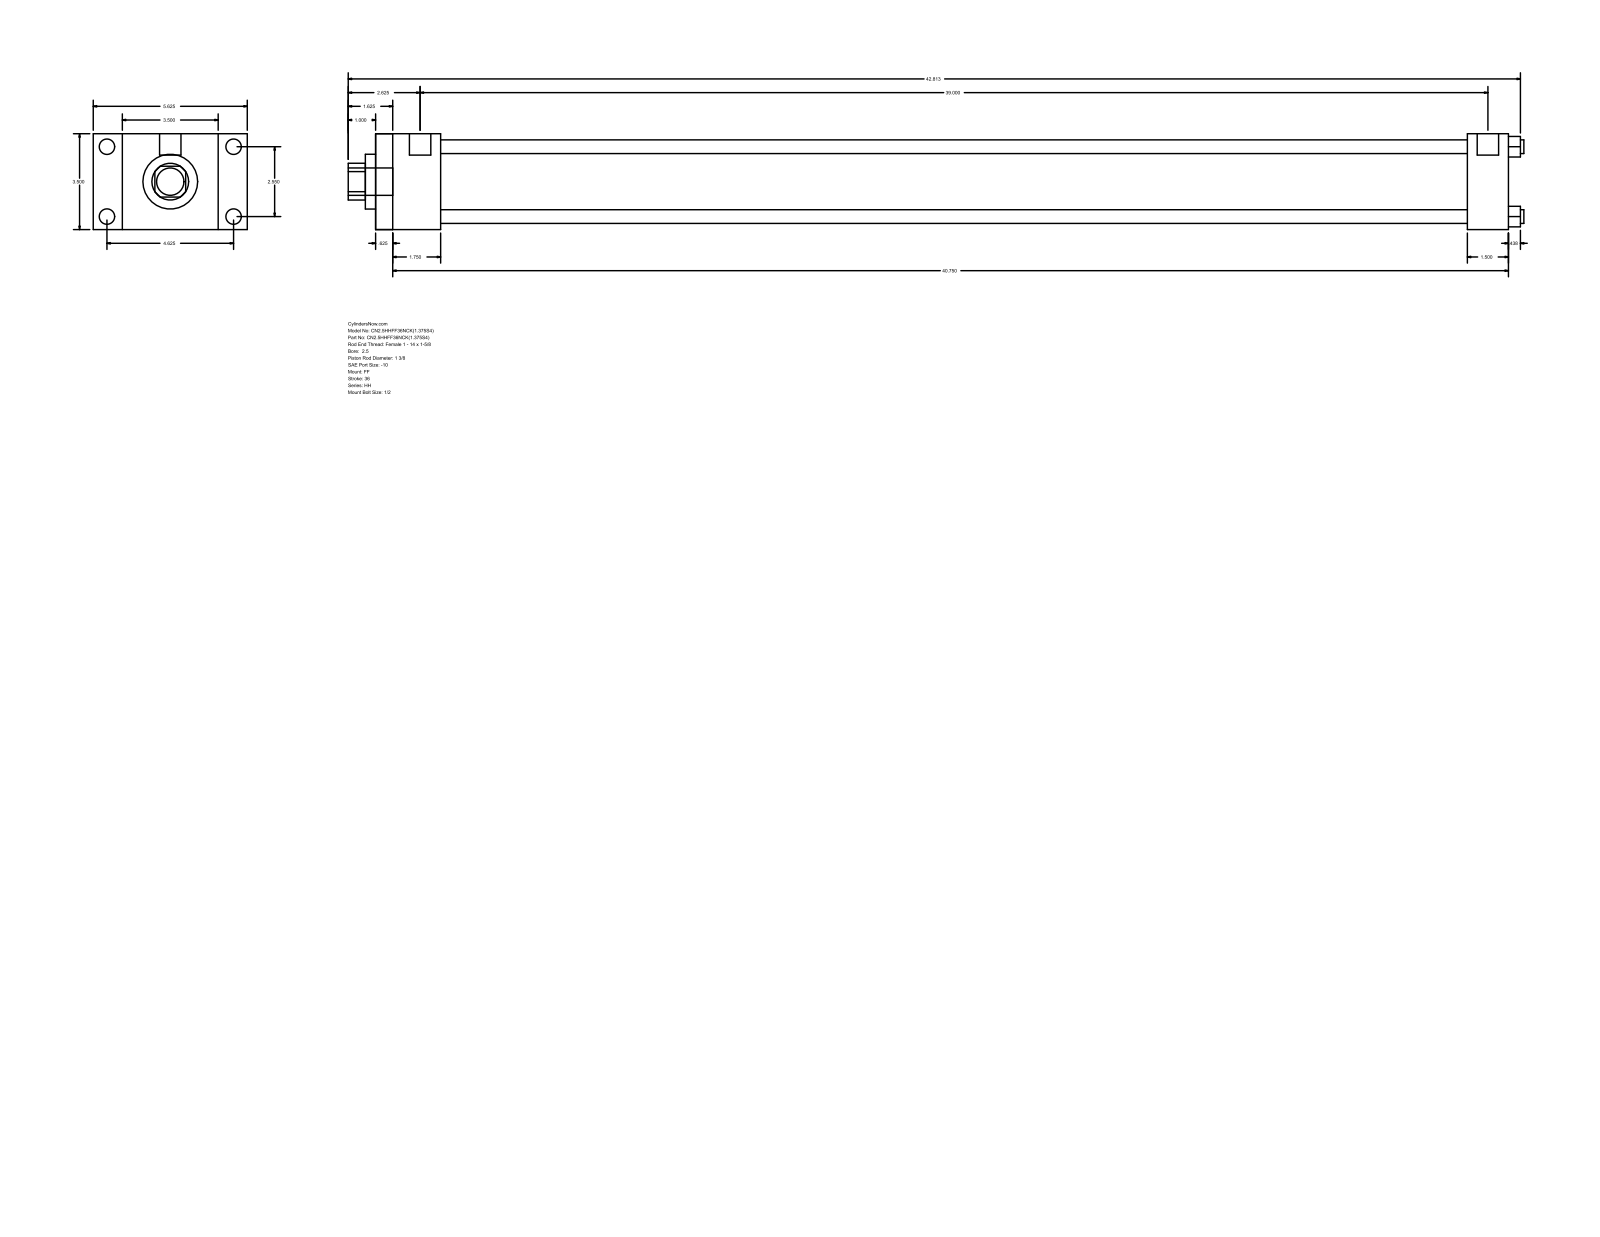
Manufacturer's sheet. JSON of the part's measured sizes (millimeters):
{"part_name": "HH_FF__0250_1.375", "step_written_by": "GSSL Pune (CONFIG_CONTROL_DESIGN)", "units": "millimeters", "bodies": {"solids": 0, "faces": 92, "planar": 64, "cylindrical": 28, "other": 0}, "overall_size": [1090.61, 142.88, 88.9], "round_holes": [[12.7, 4], [34.92, 1], [50.8, 1], [73.03, 1]], "round_bosses_or_shafts": [[14.3, 4], [5.56, 4], [19.84, 2], [25.4, 1]], "partial_cylinders_radius": [[17.06, 1]], "face_to_face_distances": [88.9, 1050.93, 15.87, 1035.06, 60.32, 44.45, 990.61, 1012.82, 996.95, 952.5], "hole_center_spacings": [45.79, 64.76, 91.58]}
